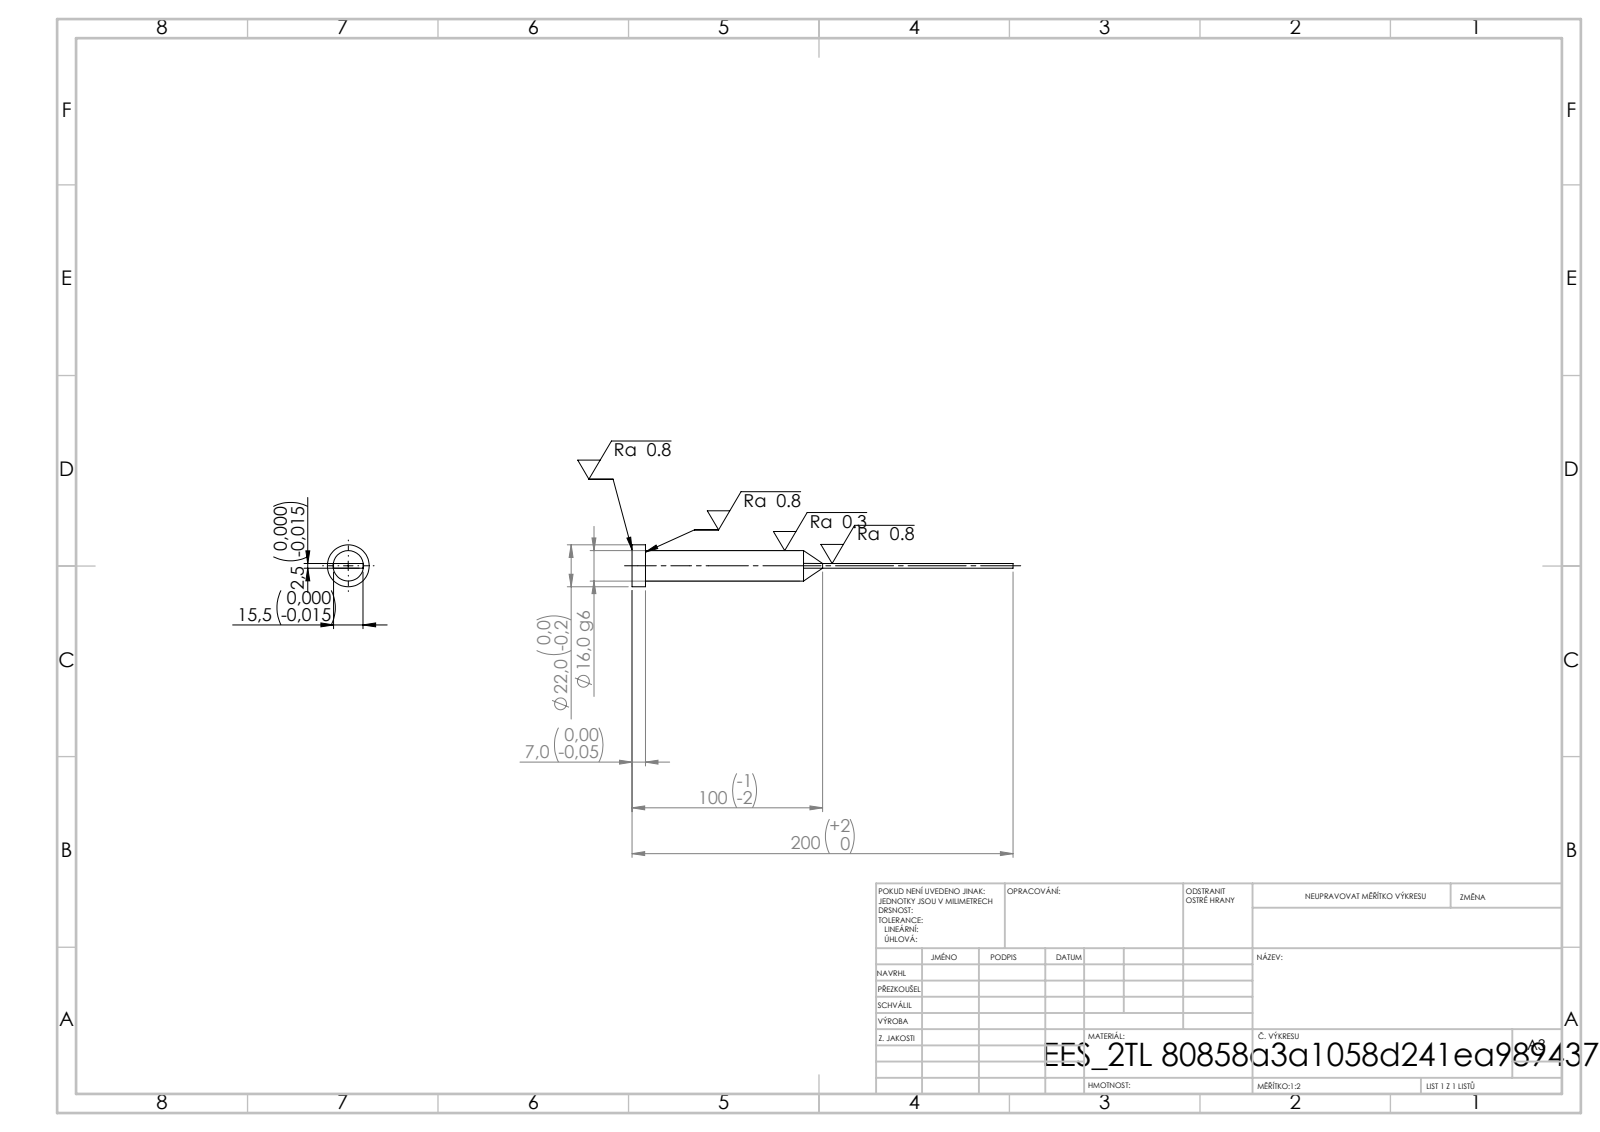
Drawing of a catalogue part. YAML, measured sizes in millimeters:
step_written_by: "SolidWorks 2019 (CONFIG_CONTROL_DESIGN)"
units: millimeters
bodies: {solids: 1, faces: 15, planar: 7, cylindrical: 4, other: 4}
overall_size: [200, 22, 22]
volume: 24361
surface_area: 9304
round_bosses_or_shafts:
  - {diameter: 22, count: 1}
  - {diameter: 16, count: 1}
face_to_face_distances: [2.5, 15.5, 7, 200, 193]
